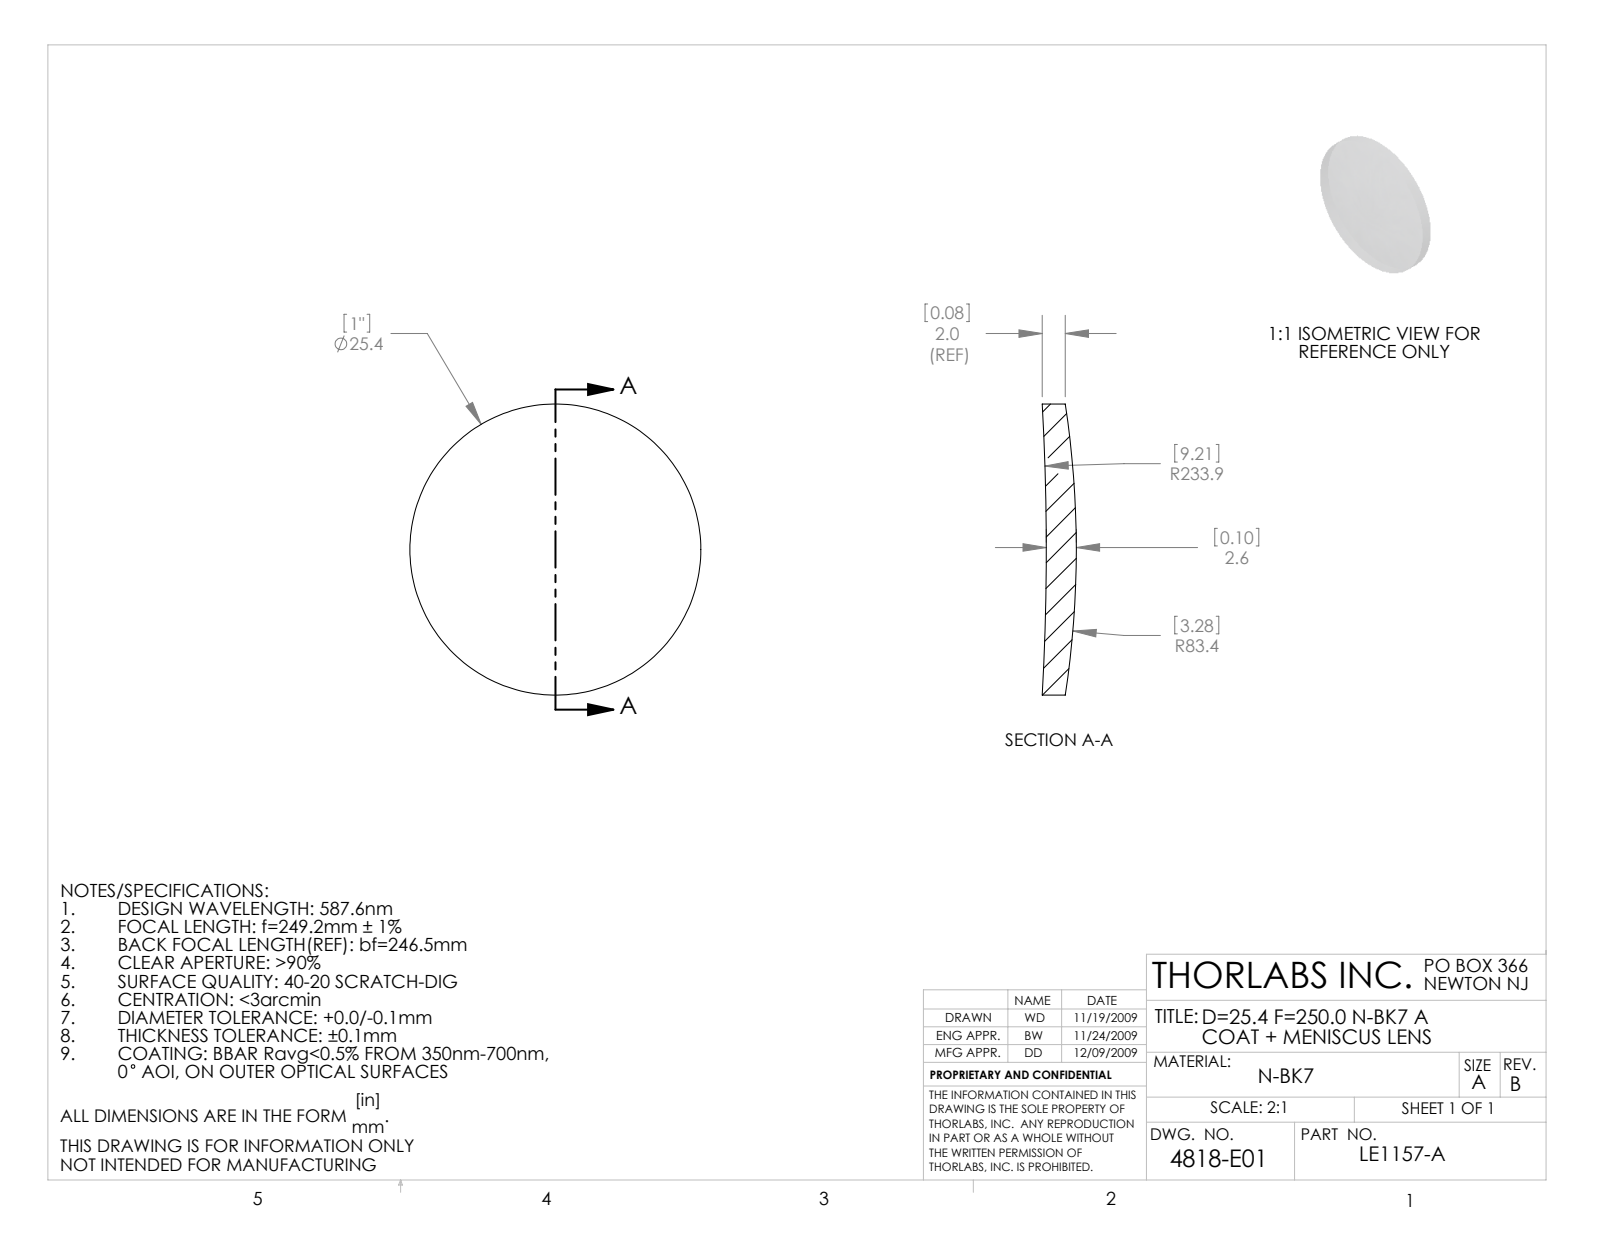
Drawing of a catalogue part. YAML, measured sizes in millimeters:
part_name: "4818-E0W"
step_written_by: "SolidWorks 2009 (AUTOMOTIVE_DESIGN)"
units: millimeters
bodies: {solids: 1, faces: 6, planar: 0, cylindrical: 2, other: 4}
overall_size: [25.4, 25.4, 2.98]
volume: 1174
surface_area: 1177
round_bosses_or_shafts:
  - {diameter: 25.4, count: 1}
